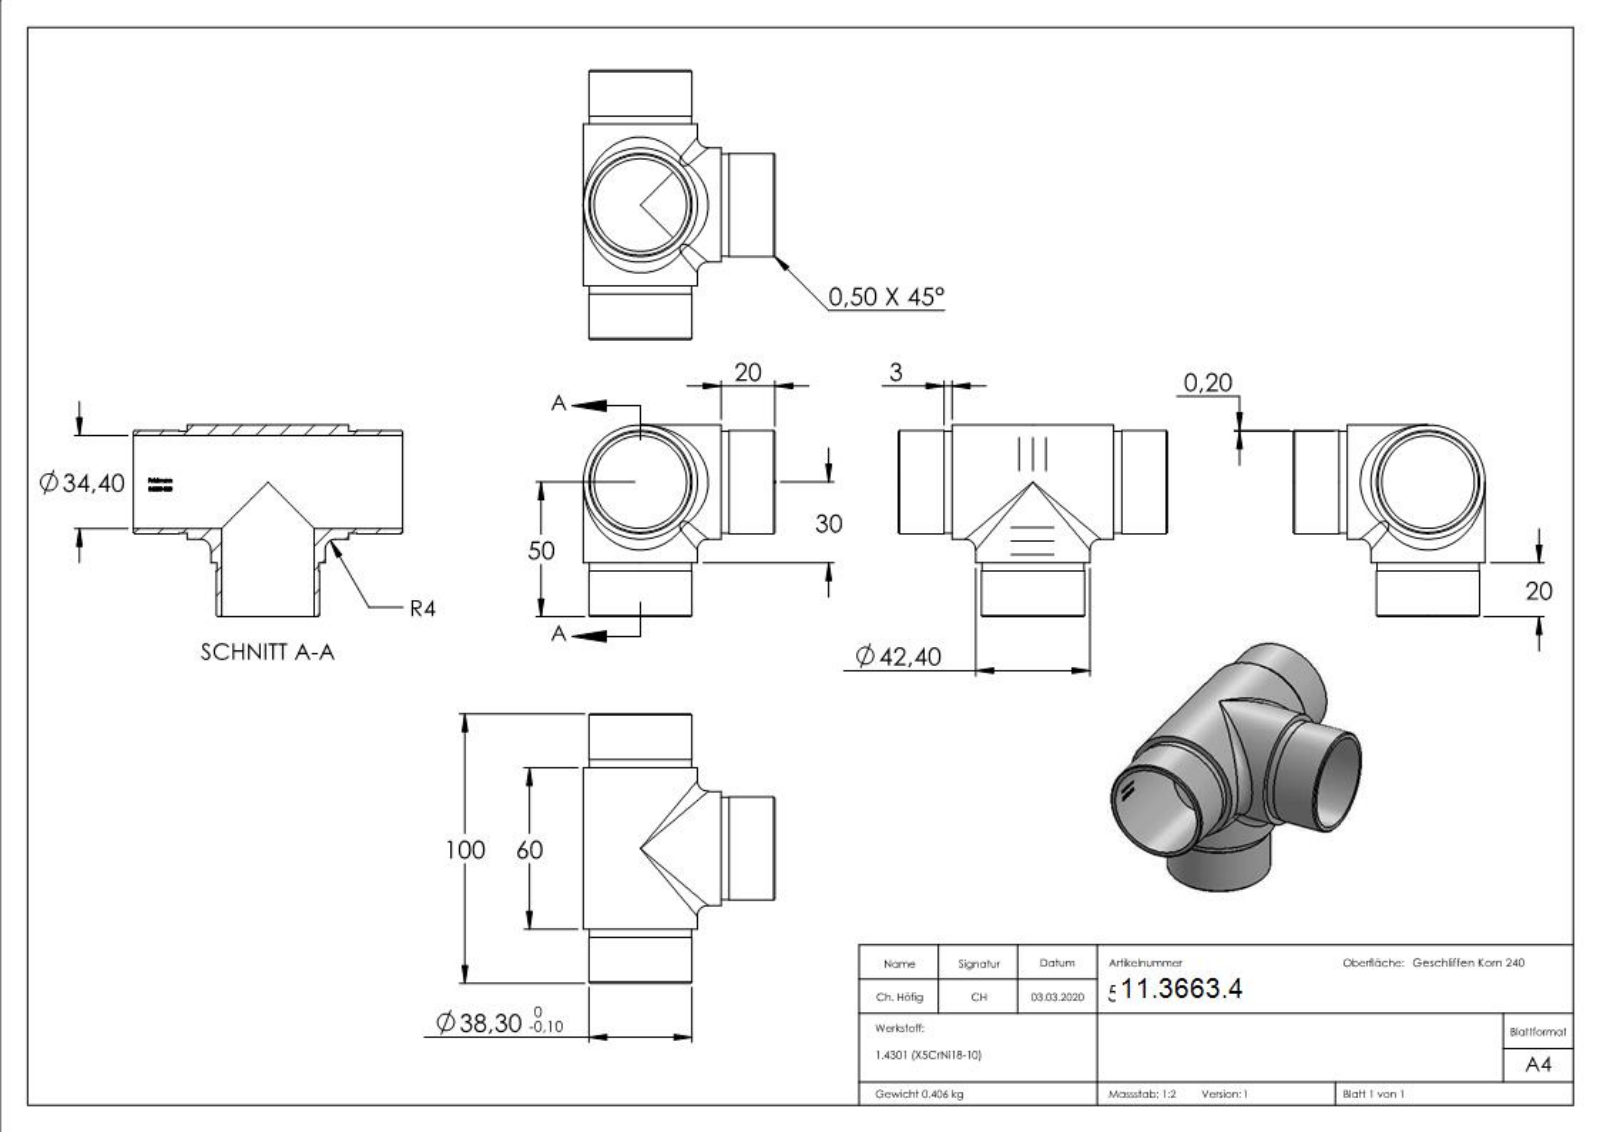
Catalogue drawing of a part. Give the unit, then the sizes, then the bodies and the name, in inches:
Units: inches
Overall size (bounding box): 3.937 × 2.803 × 2.803
Round holes (diameter × count): ⌀1.354 ×3
Round bosses / shafts (diameter × count): ⌀1.669 ×3, ⌀1.508 ×3, ⌀1.492 ×3
Partial cylindrical surfaces — rounded edges, fillets, slot ends (radius × count): R0.681 ×1
Main face-to-face distances: 0.787, 3.15, 2.362, 3.937, 0.118, 0.669, 3.268, 2.48, 2.598, 0.015
Volume: 3.137 in³ · Surface area: 56.91 in²
Bodies: 1 solid, 265 faces (100 planar, 37 cylindrical, 128 other)
Part name (STEP PRODUCT): 56205-320
STEP written by: SolidWorks 2015 (CONFIG_CONTROL_DESIGN)
